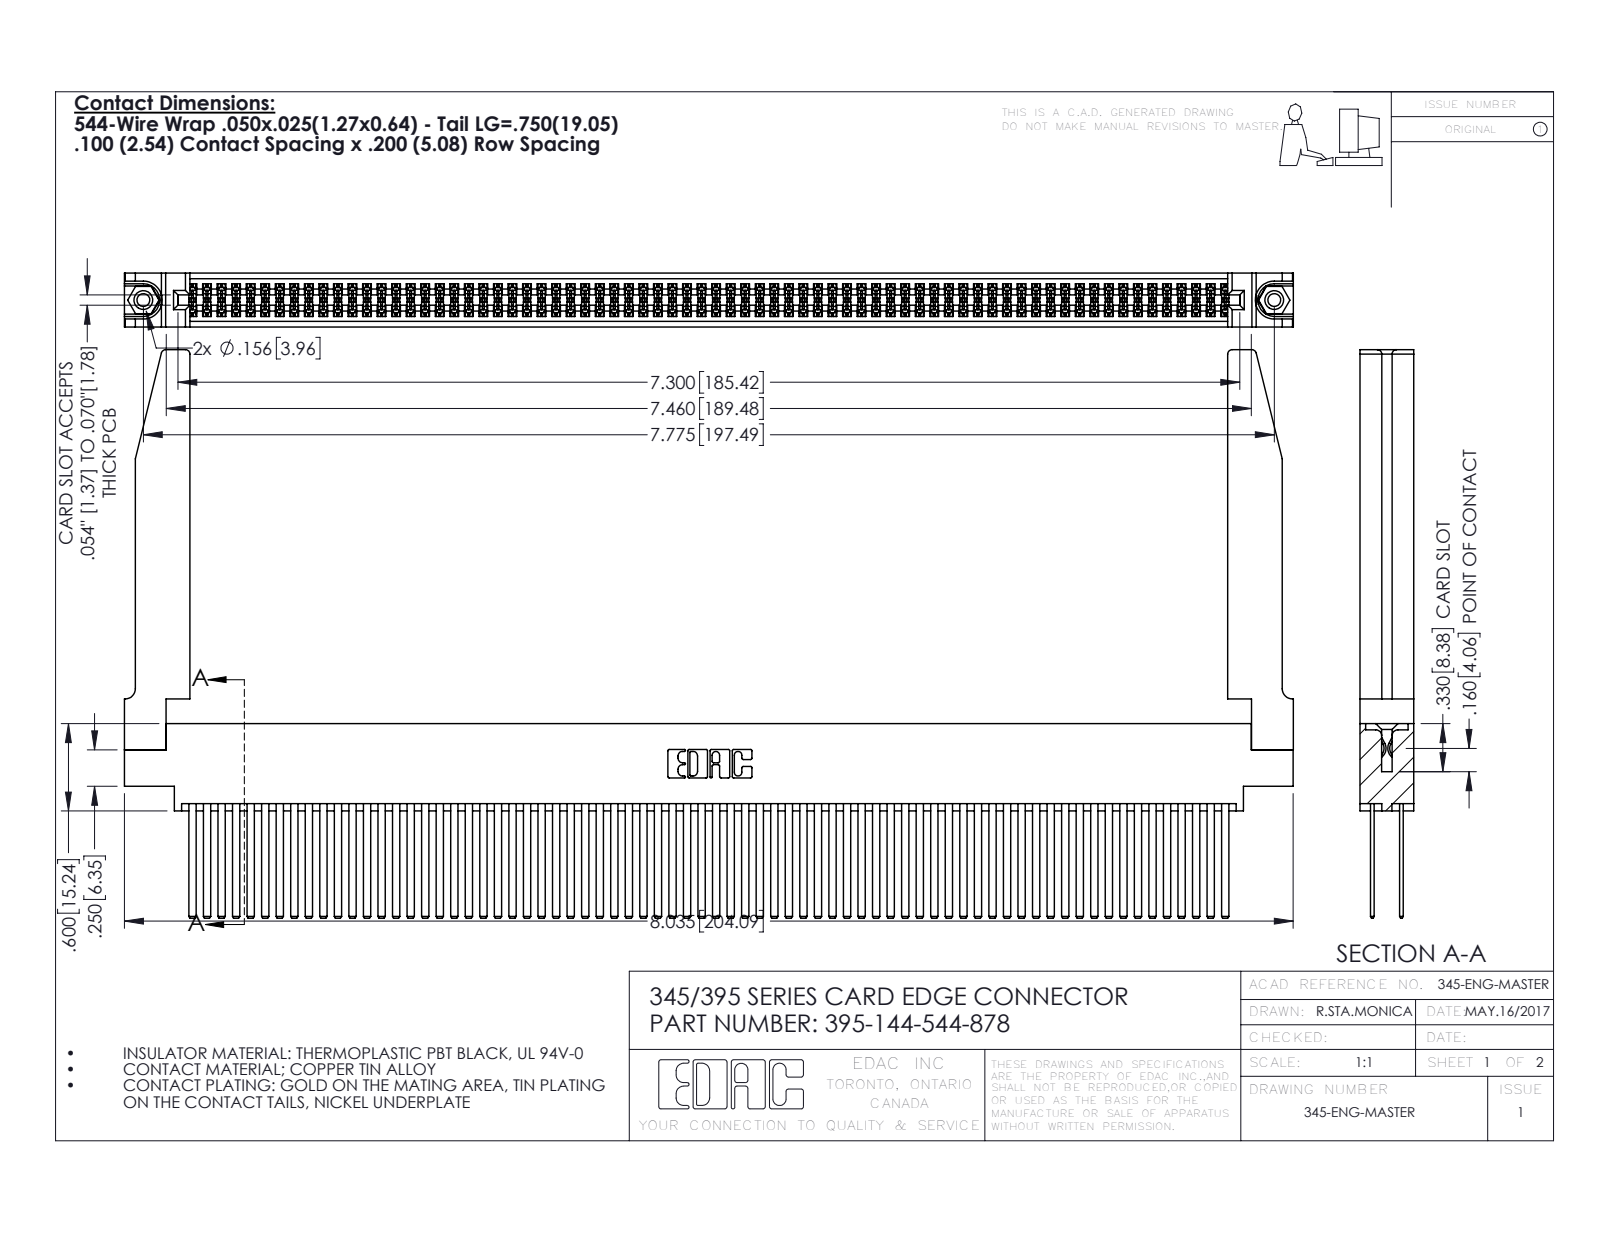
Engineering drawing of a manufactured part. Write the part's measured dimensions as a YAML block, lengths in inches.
part_name: "345-250-001_345-250-001-102; 345-220-078_345-220-078; 345-292-001_345-293-144; 395-144-544-878 (+1 more)"
step_written_by: "SolidWorks 2016 (CONFIG_CONTROL_DESIGN)"
units: inches
bodies: {solids: 149, faces: 6700, planar: 4402, cylindrical: 2246, other: 52}
overall_size: [8.036, 3.907, 0.37]
volume: 1.817
surface_area: 71.33
round_holes:
  - {diameter: 0.089, count: 2}
  - {diameter: 0.125, count: 2}
  - {diameter: 0.156, count: 2}
  - {diameter: 0.064, count: 1}
round_bosses_or_shafts:
  - {diameter: 0.155, count: 2}
partial_cylinders:
  - {radius: 0.006, count: 216}
  - {radius: 0.01, count: 22}
  - {radius: 0.03, count: 8}
  - {radius: 0.007, count: 6}
  - {radius: 0.031, count: 6}
  - {radius: 0.026, count: 3}
  - {radius: 0.014, count: 2}
  - {radius: 0.019, count: 2}
face_to_face_distances: [0.072, 0.298, 0.098, 0.272, 0.025, 0.2, 0.37, 0.225, 0.175, 0.149]
hole_center_spacings: [0.27, 7.539, 7.775]
